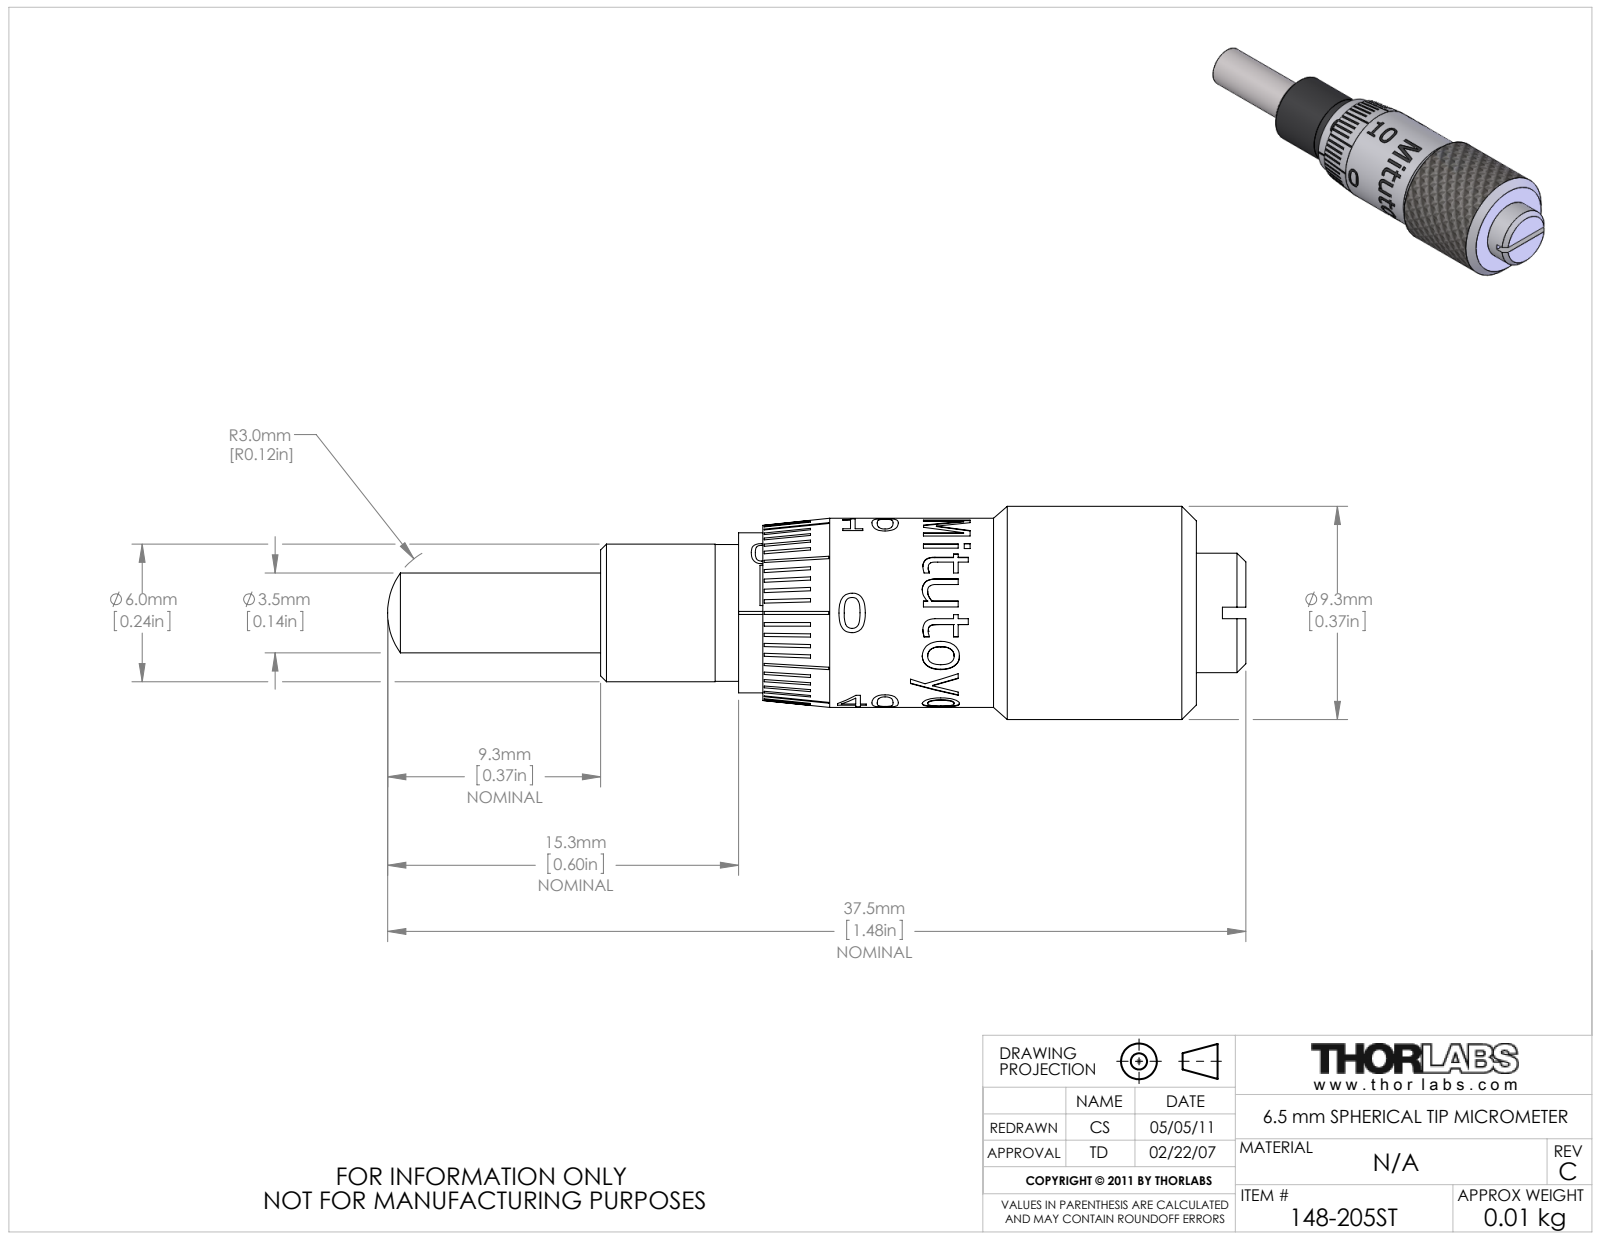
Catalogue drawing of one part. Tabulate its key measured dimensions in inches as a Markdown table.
| quantity | value |
| --- | --- |
| part name | 13429-E0W |
| STEP written by | SolidWorks 2012 (AUTOMOTIVE_DESIGN) |
| units | inches |
| bodies | 2 solids, 243 faces (67 planar, 67 cylindrical, 109 other) |
| overall size | 1.475 × 0.366 × 0.366 |
| volume | 0.102 in³ |
| surface area | 2.673 in² |
| round holes (diameter × count) | 0.138 × 1, 0.175 × 1, 0.285 × 1 |
| round bosses / shafts (diameter × count) | 0.366 × 1, 0.325 × 1, 0.275 × 1, 0.255 × 1, 0.236 × 1, 0.235 × 1, 0.205 × 1, 0.137 × 1 |
| partial cylindrical surfaces (radius × count) | 0.161 × 1 |
| main face-to-face distances | 0.565, 0.459, 1.024, 0.085, 0.65, 1.109, 0.289, 0.204, 0.361, 0.82 |
